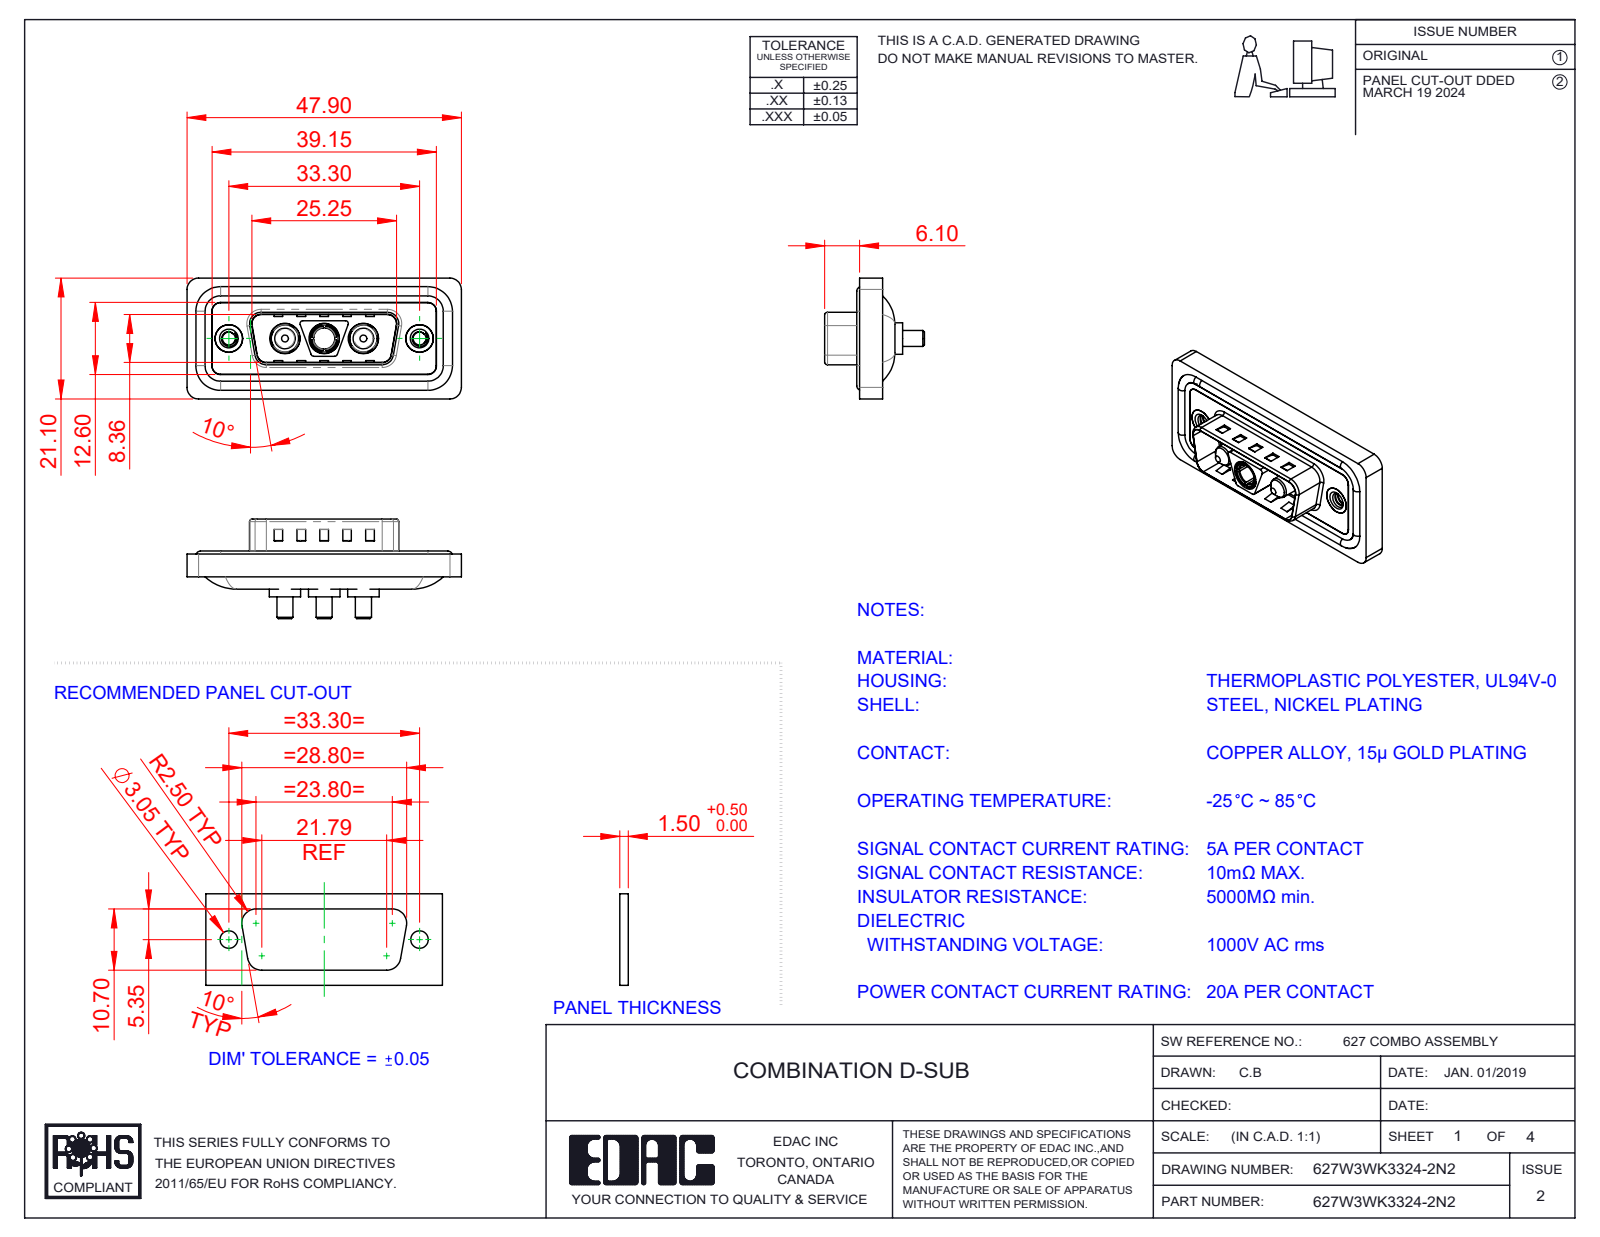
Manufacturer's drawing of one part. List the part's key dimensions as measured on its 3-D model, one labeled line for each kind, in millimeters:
Part name (STEP PRODUCT): 627Combo Threaded Rivet_2; Power Pin_20A S; 627Combo Shell Front_15 Contacts; 627Combo Housing_3WK3 (+4 more)
STEP written by: SolidWorks 2023 (CONFIG_CONTROL_DESIGN)
Units: millimetres
Bodies: 13 solids, 609 faces (231 planar, 250 cylindrical, 128 other)
Overall size (bounding box): 47.9 × 21.1 × 17.4
Volume: 5 688 mm³ · Surface area: 9 127 mm²
Round holes (diameter × count): ⌀4.85 ×3, ⌀5.3 ×3, ⌀2.26 ×2, ⌀4 ×2, ⌀4.8 ×2, ⌀5 ×2, ⌀3.7 ×1
Round bosses / shafts (diameter × count): ⌀1.6 ×4, ⌀5.5 ×3, ⌀5.2 ×3, ⌀4.75 ×3, ⌀3.75 ×3, ⌀2.8 ×3, ⌀4.9 ×2, ⌀3.6 ×2
Partial cylindrical surfaces — rounded edges, fillets, slot ends (radius × count): R1.5 ×26, R2 ×20, R0.5 ×12, R1.6 ×8, R0.25 ×4, R0.6 ×4, R0.65 ×4, R0.9 ×4
Main face-to-face distances: 0.4, 1.1, 1.5, 0.5, 1.6, 3.1, 2.9, 4, 0.82, 9.58
Hole centre spacings: 6.85, 9.8, 16.65, 23.5, 13.7, 33.3
